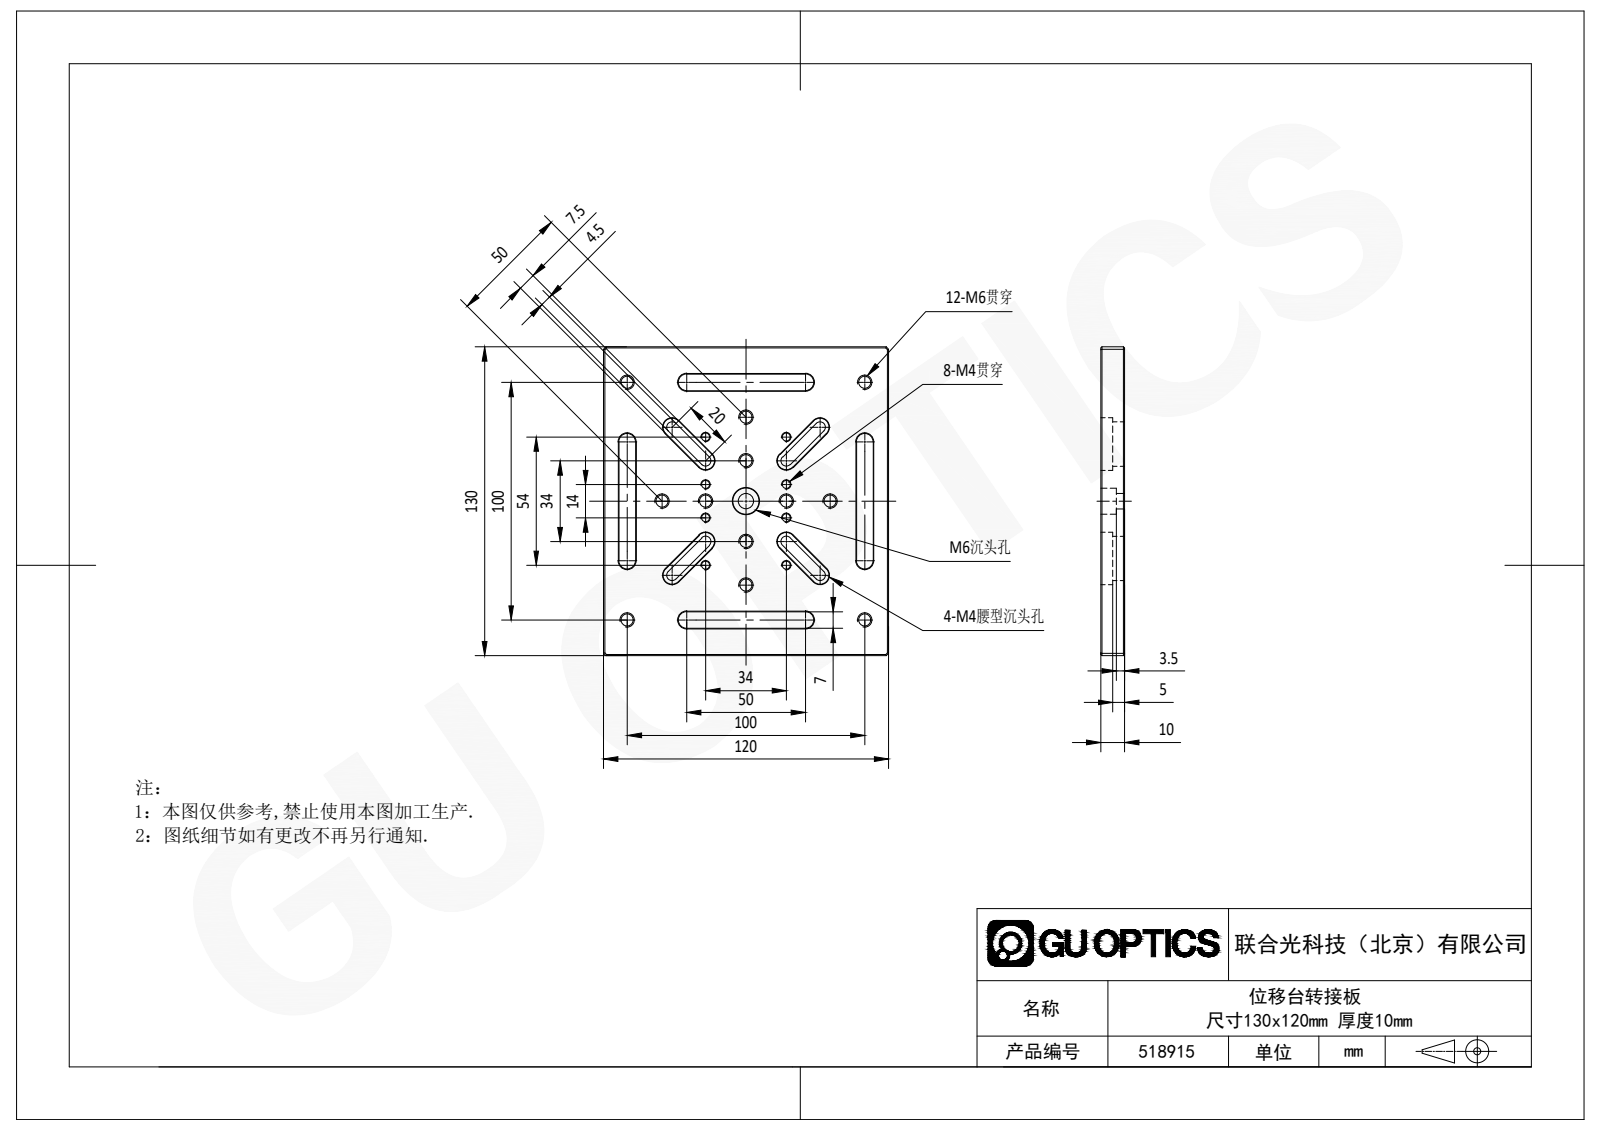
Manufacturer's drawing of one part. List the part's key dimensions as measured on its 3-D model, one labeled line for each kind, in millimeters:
STEP written by: SolidWorks 2020 (CONFIG_CONTROL_DESIGN)
Units: millimetres
Bodies: 1 solid, 154 faces (71 planar, 46 cylindrical, 37 other)
Overall size (bounding box): 130 × 120 × 10
Volume: 130 482 mm³ · Surface area: 41 311 mm²
Round holes (diameter × count): ⌀5 ×12, ⌀3.3 ×8, ⌀6.5 ×1, ⌀11 ×1
Partial cylindrical surfaces — rounded edges, fillets, slot ends (radius × count): R2.25 ×8, R3.5 ×8, R3.75 ×8
Main face-to-face distances: 10, 7, 100, 120, 130, 6.5, 11.5, 18.5, 111.5, 118.5
Hole centre spacings: 34, 19.72, 39.23, 52.1, 59.91, 83.6, 98.93, 7
